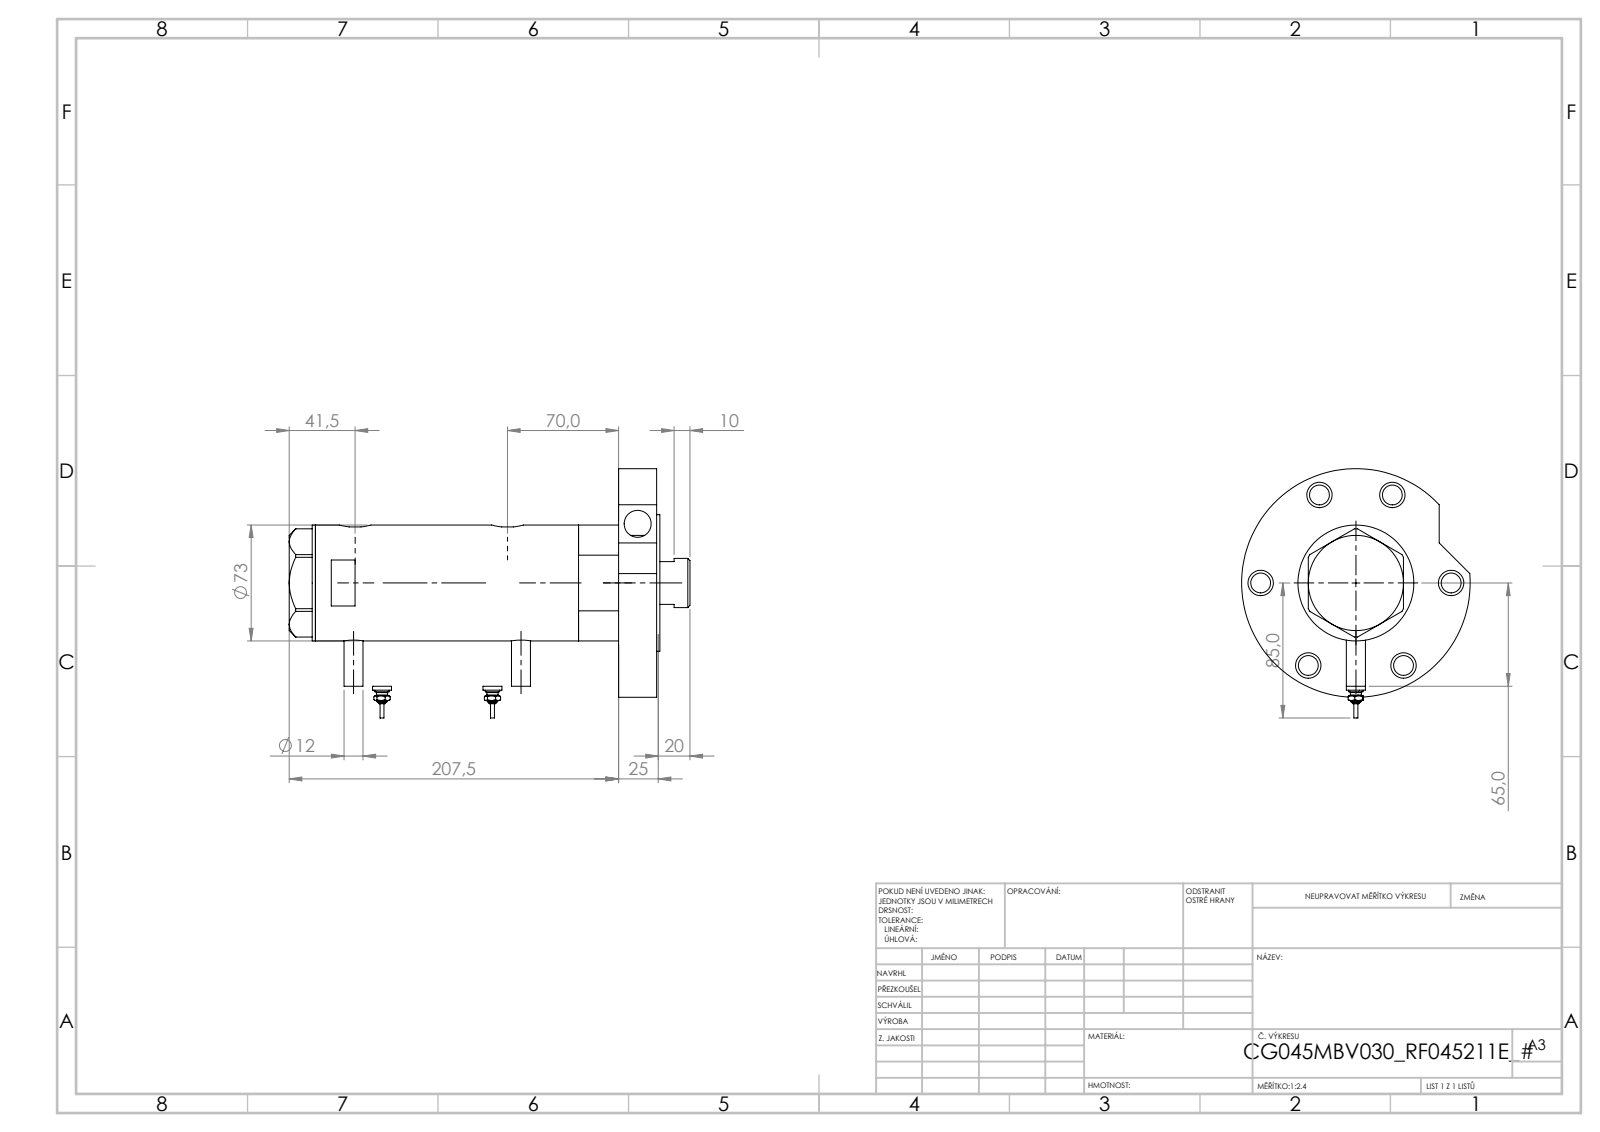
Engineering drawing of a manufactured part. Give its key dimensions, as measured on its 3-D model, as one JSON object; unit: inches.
{"part_name": "V270CG_MIDDLE; Switch; V270CG_RF211E; V270CG_FRONT (+2 more)", "step_written_by": "SolidWorks 2019 (CONFIG_CONTROL_DESIGN)", "units": "inches", "bodies": {"solids": 7, "faces": 256, "planar": 88, "cylindrical": 104, "other": 64}, "overall_size": [9.941, 6.181, 5.669], "volume_in3": 72.13, "surface_area_in2": 317.8, "round_holes": [[0.492, 8], [0.63, 6], [0.518, 2], [0.413, 1], [0.669, 1], [1.26, 1], [1.319, 1], [1.772, 1], [1.89, 1], [2.362, 1], [2.52, 1]], "round_bosses_or_shafts": [[0.472, 4], [0.354, 2], [0.276, 2], [0.177, 2], [0.098, 2], [5.669, 1], [3.386, 1], [2.874, 1]], "partial_cylinders_radius": [[0.394, 2]], "face_to_face_distances": [0.945, 7.52, 1.024, 3.74, 0.079, 8.465, 8.543, 0.039, 4.764, 2.756], "hole_center_spacings": [2.362, 2.625, 3.928, 4.091, 4.237, 4.714, 0.039, 0.335]}
